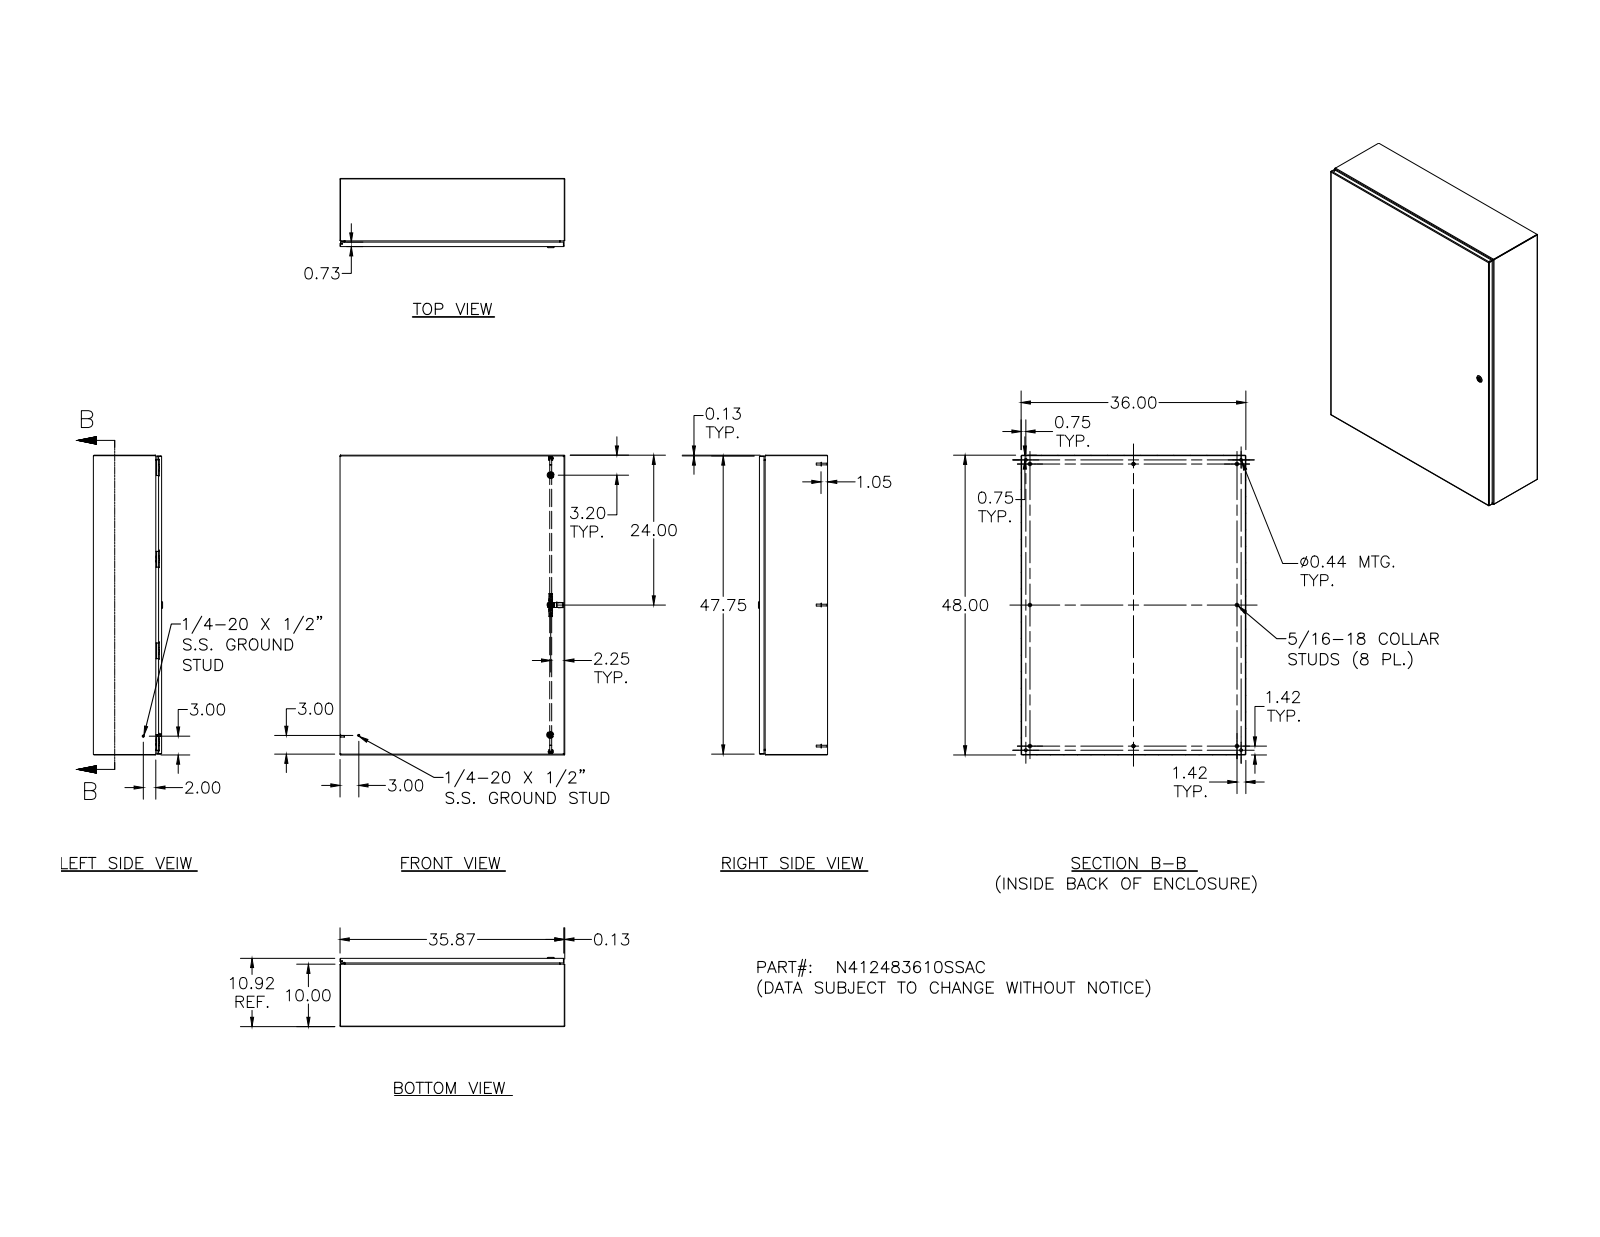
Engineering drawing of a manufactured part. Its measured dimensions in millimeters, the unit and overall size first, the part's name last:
Units: millimetres
Overall size (bounding box): 1219.2 × 914.4 × 281.3
Round holes (diameter × count): ⌀2.4 ×8, ⌀3.9 ×8, ⌀4.2 ×8, ⌀4.4 ×8, ⌀4.7 ×8, ⌀5 ×5, ⌀4 ×4, ⌀4.2 ×4, ⌀11.1 ×4, ⌀2.7 ×2, ⌀4.1 ×2, ⌀4.3 ×2
Round bosses / shafts (diameter × count): ⌀6.4 ×18, ⌀14.3 ×8, ⌀9.1 ×8, ⌀8.1 ×8, ⌀7.6 ×8, ⌀7 ×8, ⌀6.5 ×8, ⌀4.2 ×8
Partial cylindrical surfaces — rounded edges, fillets, slot ends (radius × count): R1.3 ×50, R0.8 ×36, R0.4 ×34, R3.2 ×32, R0.3 ×30, R0.5 ×20, R2.7 ×18, R3 ×18
Main face-to-face distances: 1.9, 275.4, 273.5, 277.3, 912.5, 1217.3, 910.6, 914.4, 1215.4, 1219.2
Hole centre spacings: 372.5, 745.1, 372.5, 1117.6, 12.7, 16.7, 33.2, 372.7
Volume: 6 725 000 mm³ · Surface area: 7 143 000 mm²
Bodies: 81 solids, 2661 faces (988 planar, 992 cylindrical, 681 other)
Part name (STEP PRODUCT): N412483610SSAC; N412483610SSACBLR; N4123610SSACTB; 388151 (+8 more)
STEP written by: Autodesk Inventor 2011 (AUTOMOTIVE_DESIGN)
